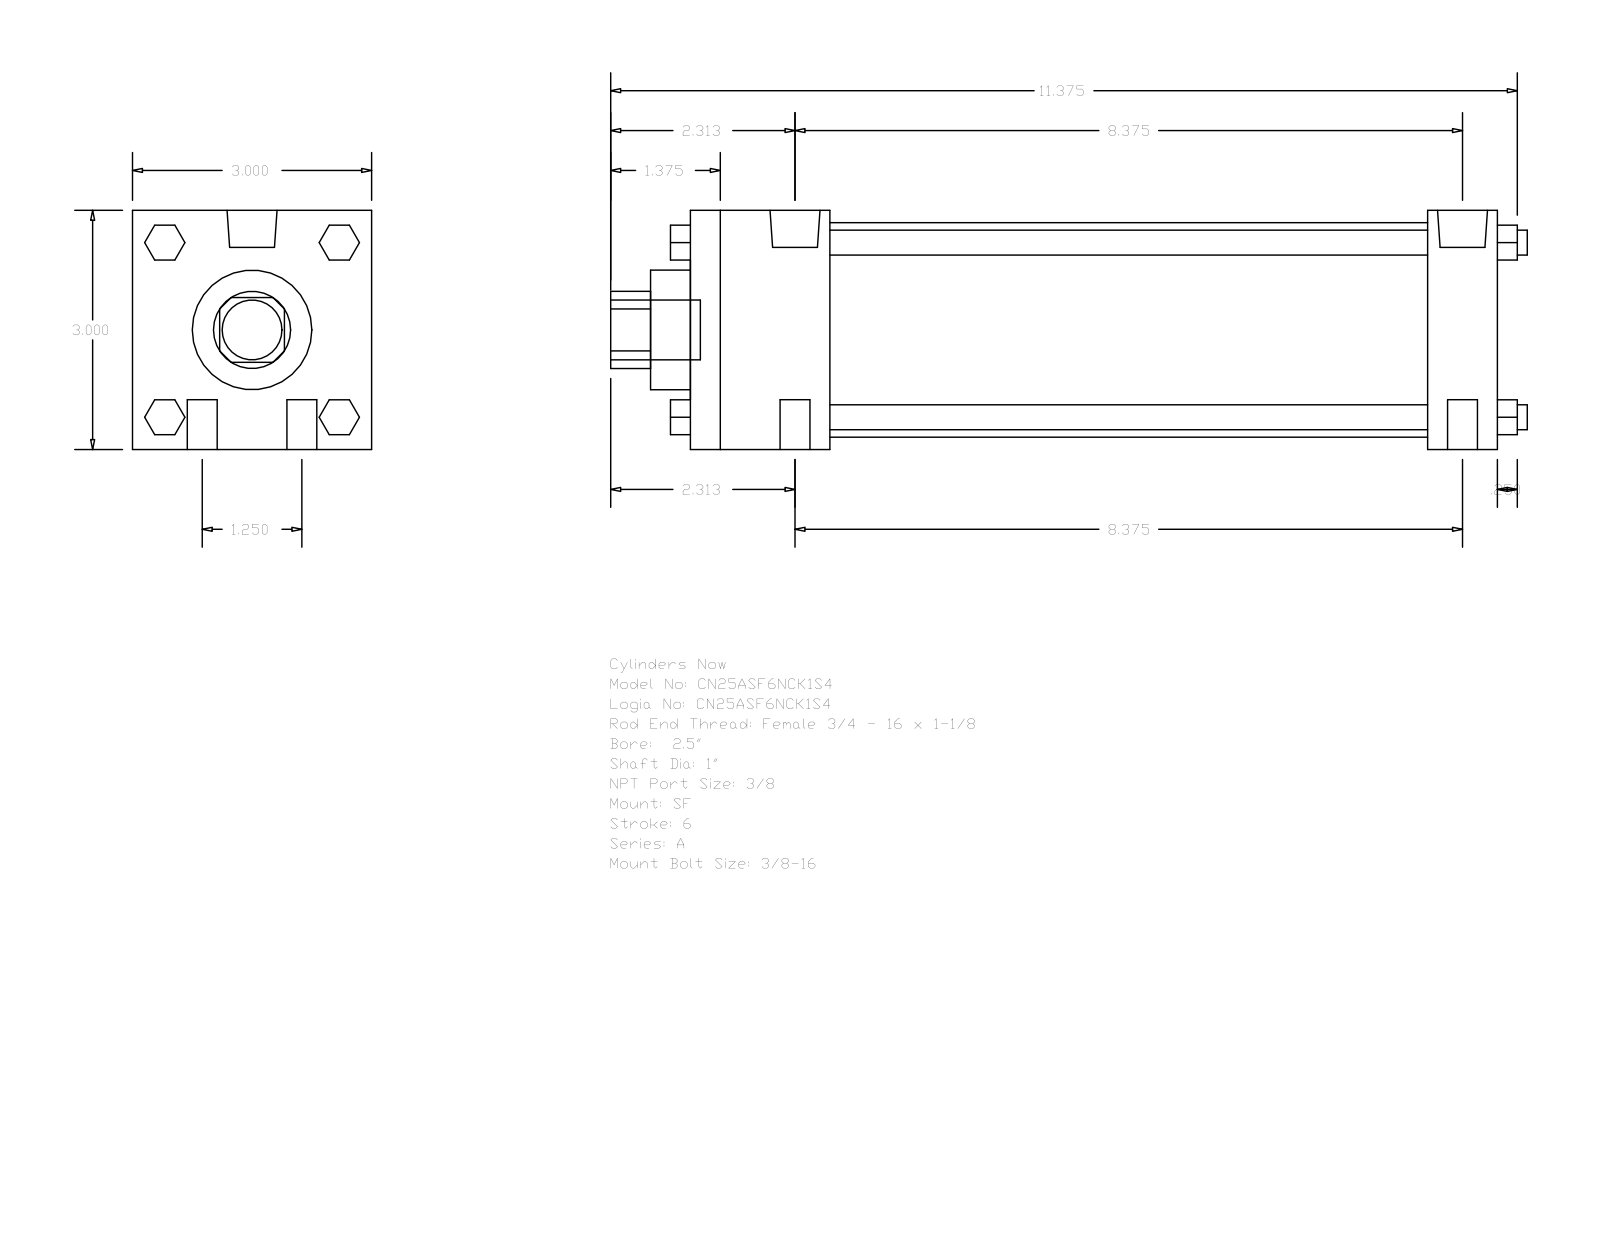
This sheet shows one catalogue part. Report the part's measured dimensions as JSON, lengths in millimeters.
{"part_name": "A_SF__0250_1", "step_written_by": "GSSL Pune (CONFIG_CONTROL_DESIGN)", "units": "millimeters", "bodies": {"solids": 0, "faces": 124, "planar": 94, "cylindrical": 30, "other": 0}, "overall_size": [292.1, 76.2, 76.2], "round_holes": [[25.4, 1], [38.1, 1], [68.33, 1]], "round_bosses_or_shafts": [[9.53, 4], [7.94, 4], [15.93, 2], [5.56, 2], [19.05, 1]], "partial_cylinders_radius": [[12.29, 1]], "face_to_face_distances": [76.2, 257.17, 234.95, 22.22, 44.45, 190.5, 212.72, 12.7, 11.11, 57.15]}
